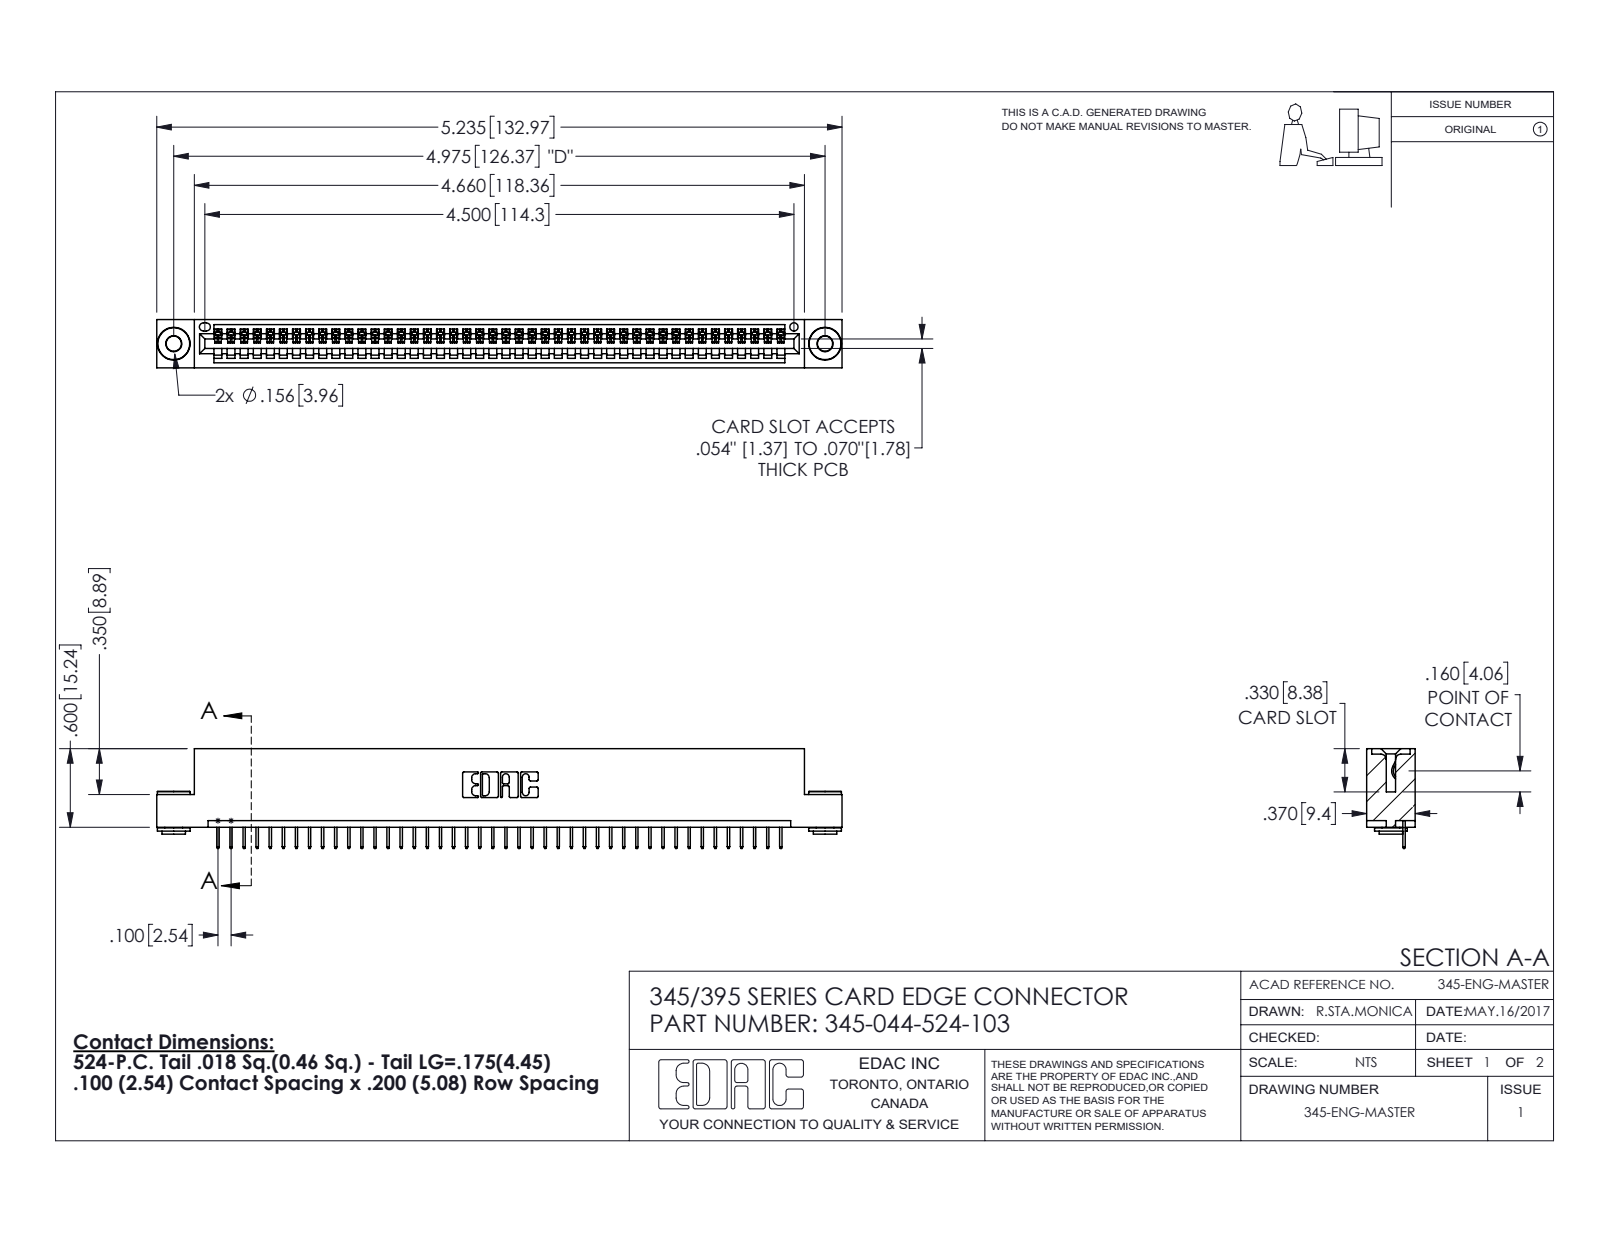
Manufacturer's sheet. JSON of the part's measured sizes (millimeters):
{"part_name": "345-250-002_345-250-002-102; 345-292-001_345-293-124; 345 Part_Flush Mounting Lugs - 0.156 Dia-TH; 345-044-524-103", "step_written_by": "SolidWorks 2016 (CONFIG_CONTROL_DESIGN)", "units": "millimeters", "bodies": {"solids": 47, "faces": 2892, "planar": 2114, "cylindrical": 770, "other": 8}, "overall_size": [133, 19.4, 9.4], "volume_mm3": 12500, "surface_area_mm2": 16280, "round_holes": [[2.9, 2], [4, 2], [1.6, 1]], "round_bosses_or_shafts": [[6.4, 2], [4.6, 2], [3.5, 2]], "partial_cylinders_radius": [[0.2, 88], [0.3, 22], [0.2, 6], [0.8, 6], [0.7, 3], [0.8, 2], [1, 2], [0.4, 1]], "face_to_face_distances": [1.8, 7.6, 9.4, 5.1, 0.6, 2.5, 6.9, 5.7, 1.8, 3.8], "hole_center_spacings": [6.9, 120.4, 126.4]}
